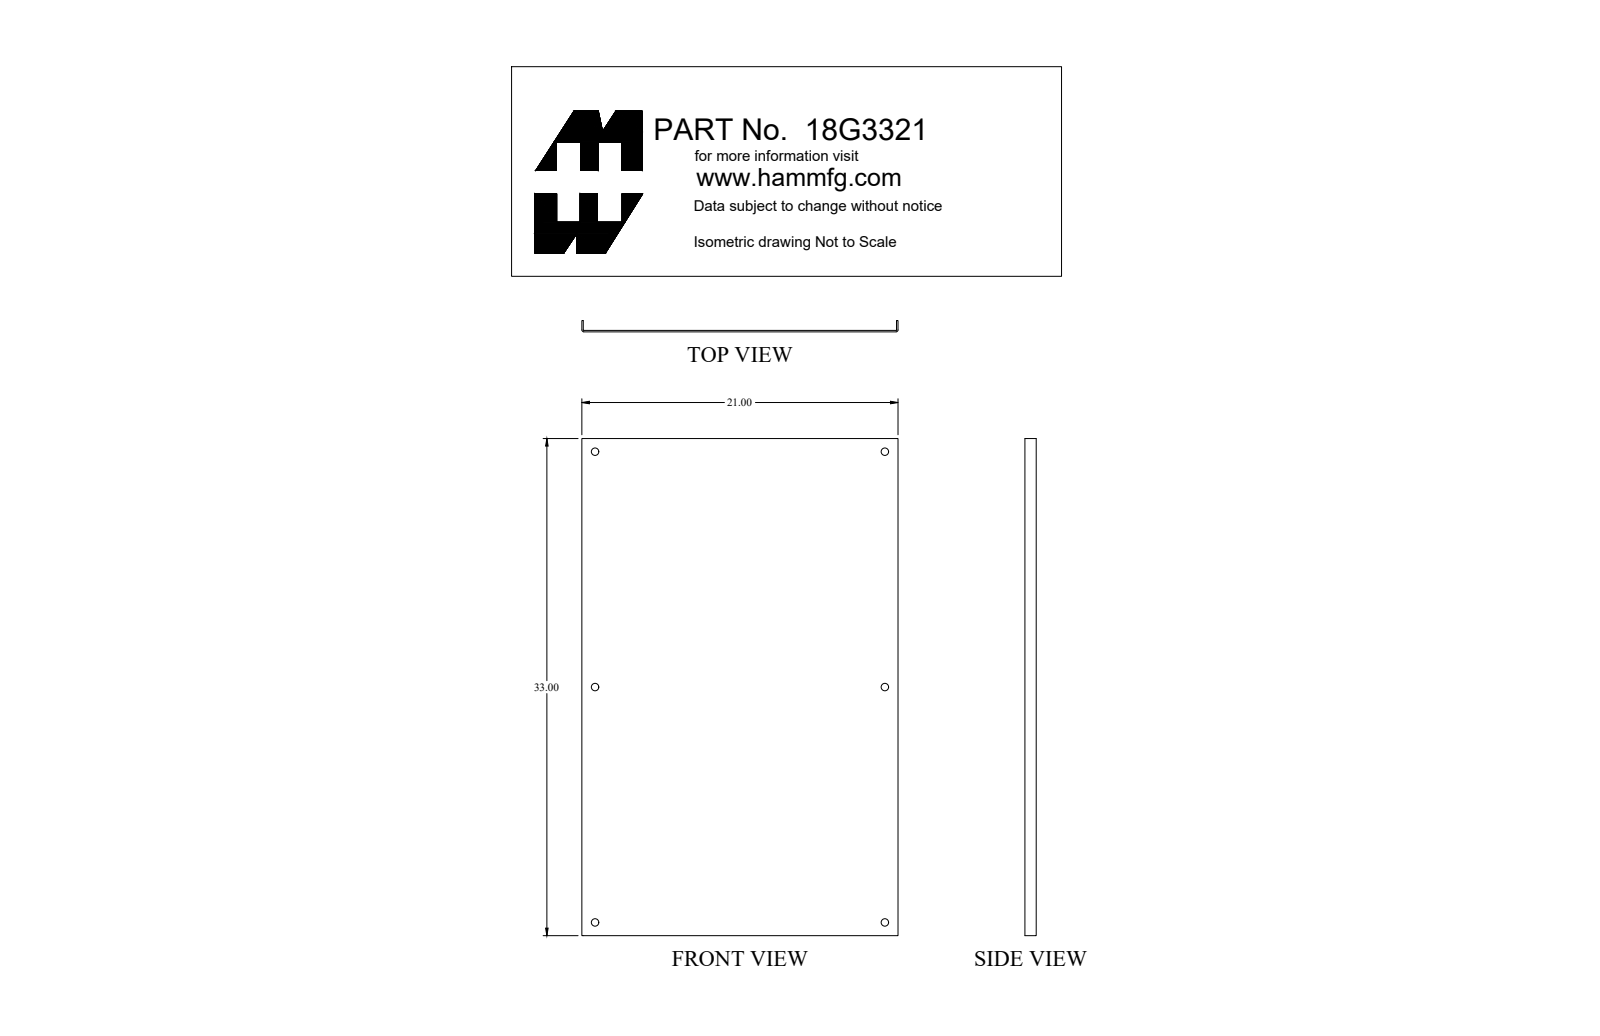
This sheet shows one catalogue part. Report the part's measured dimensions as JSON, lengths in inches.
{"part_name": "18G3321", "step_written_by": "SolidWorks 2018 (AUTOMOTIVE_DESIGN)", "units": "inches", "bodies": {"solids": 1, "faces": 20, "planar": 10, "cylindrical": 10, "other": 0}, "overall_size": [33, 21, 0.75], "volume_in3": 69.62, "surface_area_in2": 1477, "round_holes": [[0.5, 6]], "partial_cylinders_radius": [[0.03, 2], [0.125, 2]], "face_to_face_distances": [0.095, 20.905, 21, 20.81, 0.75, 0.655, 33], "hole_center_spacings": [15.625, 24.793, 19.25, 31.25, 36.703]}
